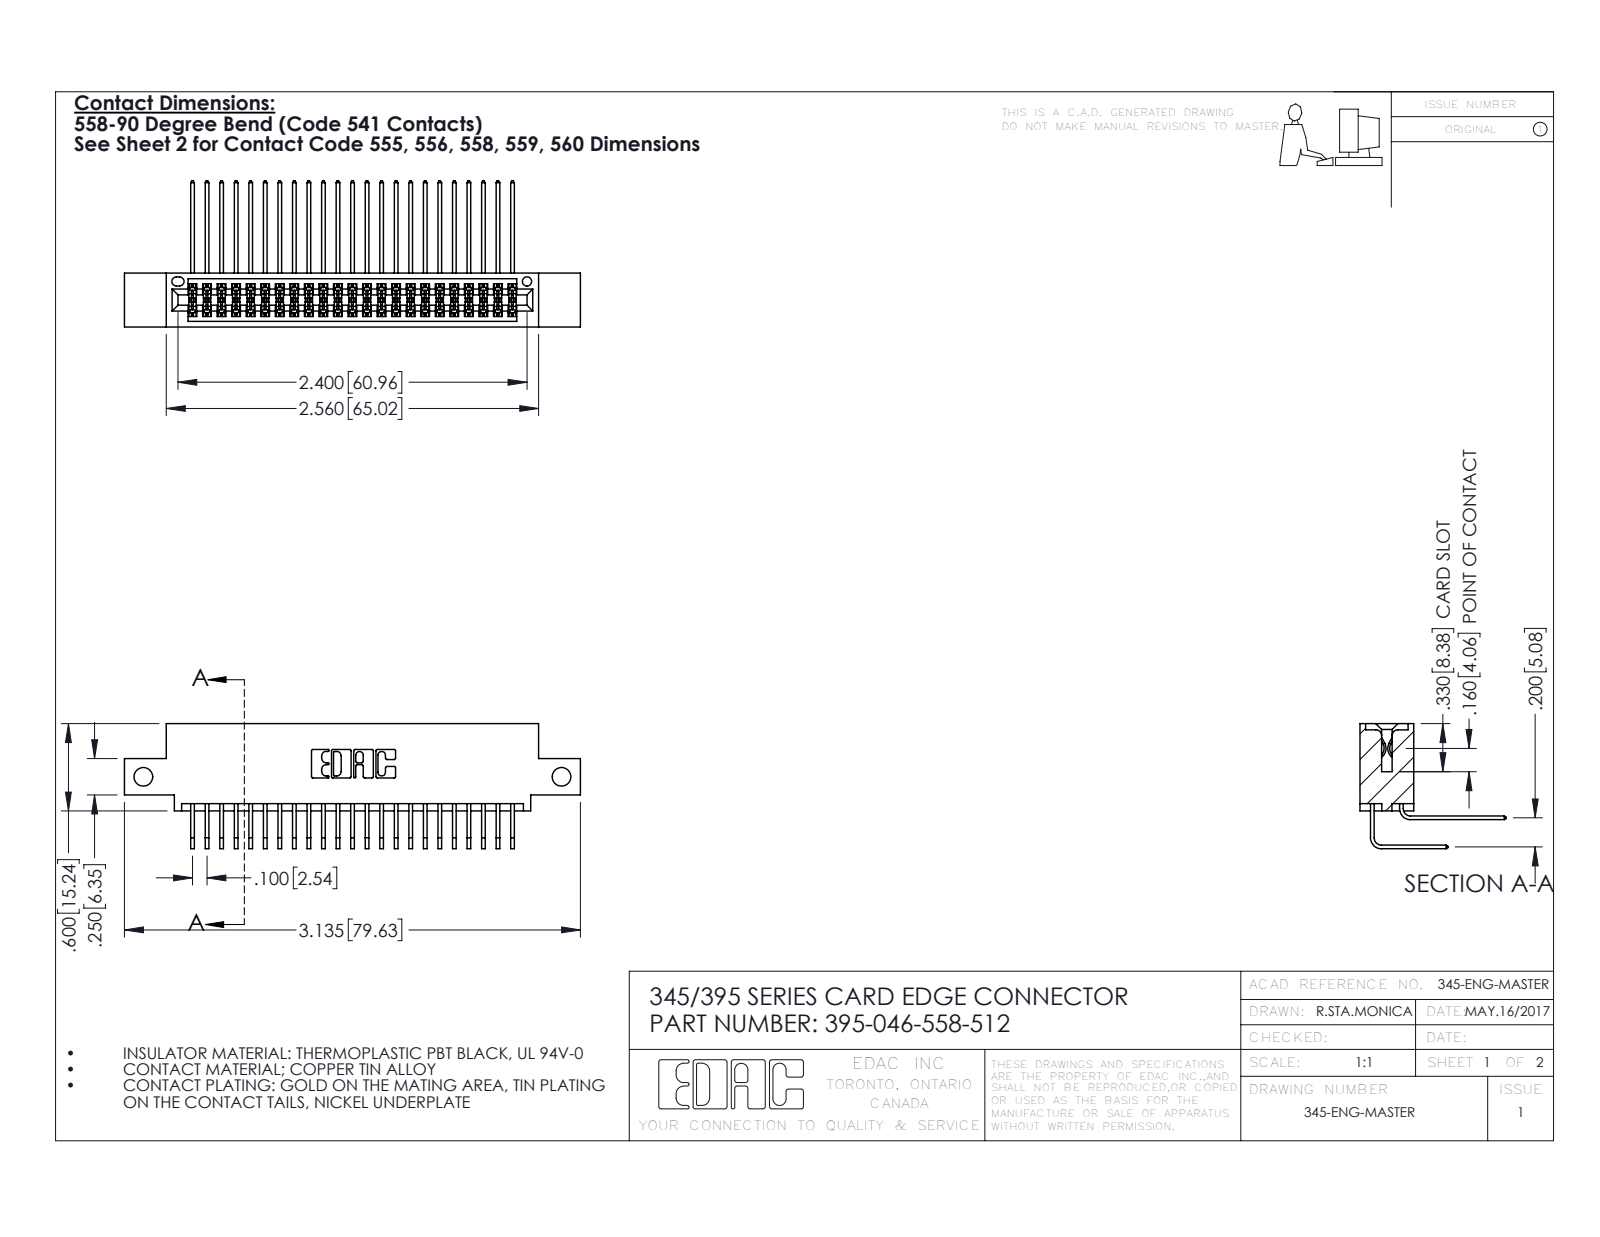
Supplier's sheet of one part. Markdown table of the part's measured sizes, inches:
| quantity | value |
| --- | --- |
| part name | 345-292-001_558 Tail - 2; 395-046-558-512; 345-292-001_558 559 Tail - 1; 345 Part_0.110 Offset - Side Mount |
| STEP written by | SolidWorks 2016 (CONFIG_CONTROL_DESIGN) |
| units | inches |
| bodies | 47 solids, 2522 faces (1694 planar, 828 cylindrical, 0 other) |
| overall size | 3.135 × 1.005 × 0.859 |
| volume | 0.468 in³ |
| surface area | 18.86 in² |
| round holes (diameter × count) | 0.128 × 2, 0.064 × 1 |
| partial cylindrical surfaces (radius × count) | 0.006 × 70, 0.01 × 22, 0.007 × 6, 0.031 × 6, 0.026 × 3, 0.014 × 2, 0.019 × 2, 0.022 × 2 |
| main face-to-face distances | 0.072, 0.298, 0.2, 0.37, 0.098, 0.272, 0.025, 0.225, 0.025, 0.175 |
| hole center spacings | 2.875 |
